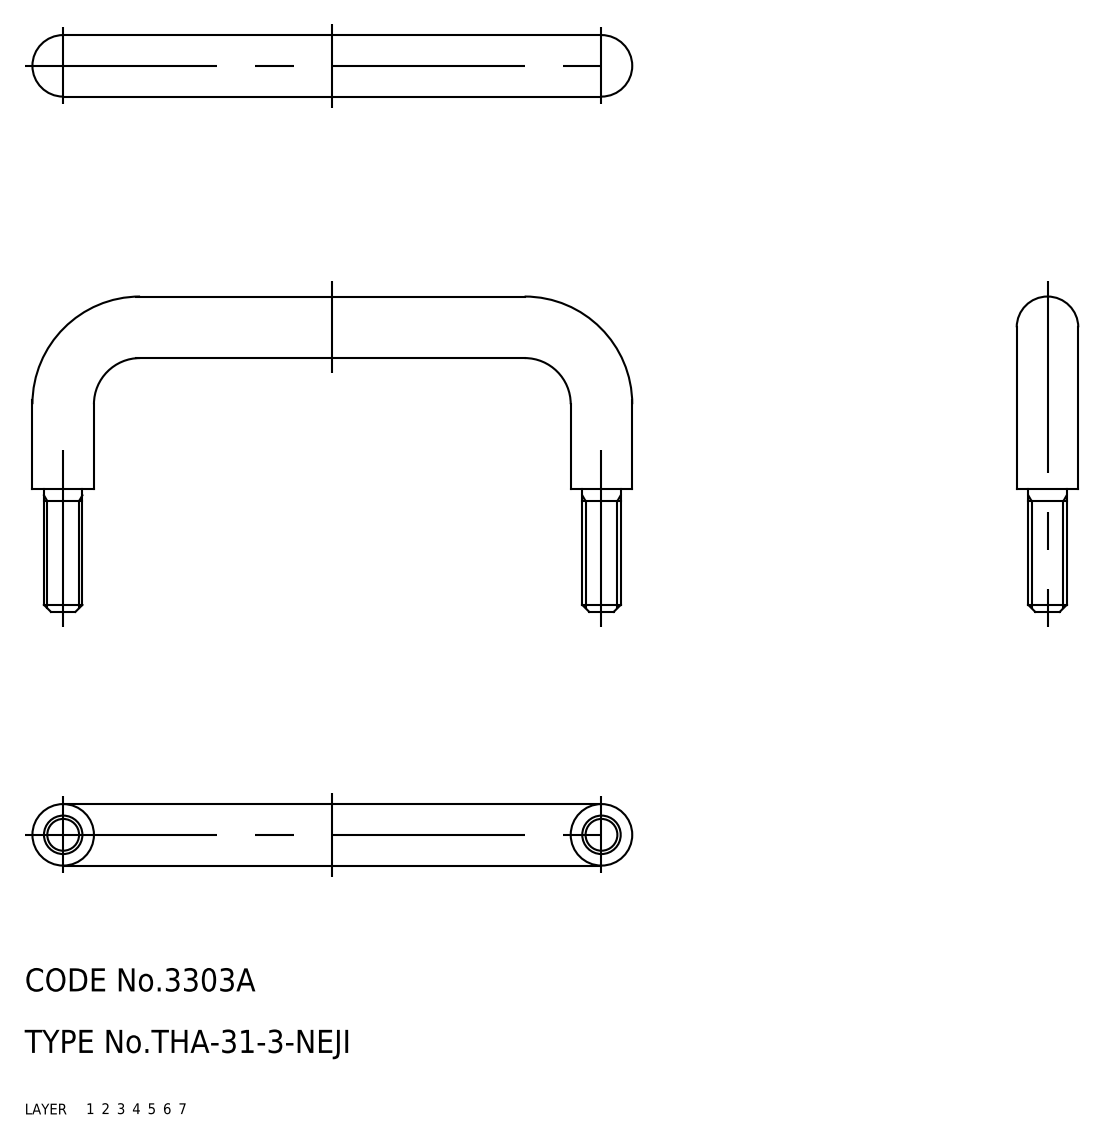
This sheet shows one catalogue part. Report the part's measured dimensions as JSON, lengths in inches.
{"part_name": "pull", "step_written_by": "CADfix (AUTOMOTIVE_DESIGN)", "units": "inches", "bodies": {"solids": 1, "faces": 22, "planar": 0, "cylindrical": 0, "other": 22}, "overall_size": [3.071, 1.614, 0.315], "volume_in3": 0.356, "surface_area_in2": 4.938}
